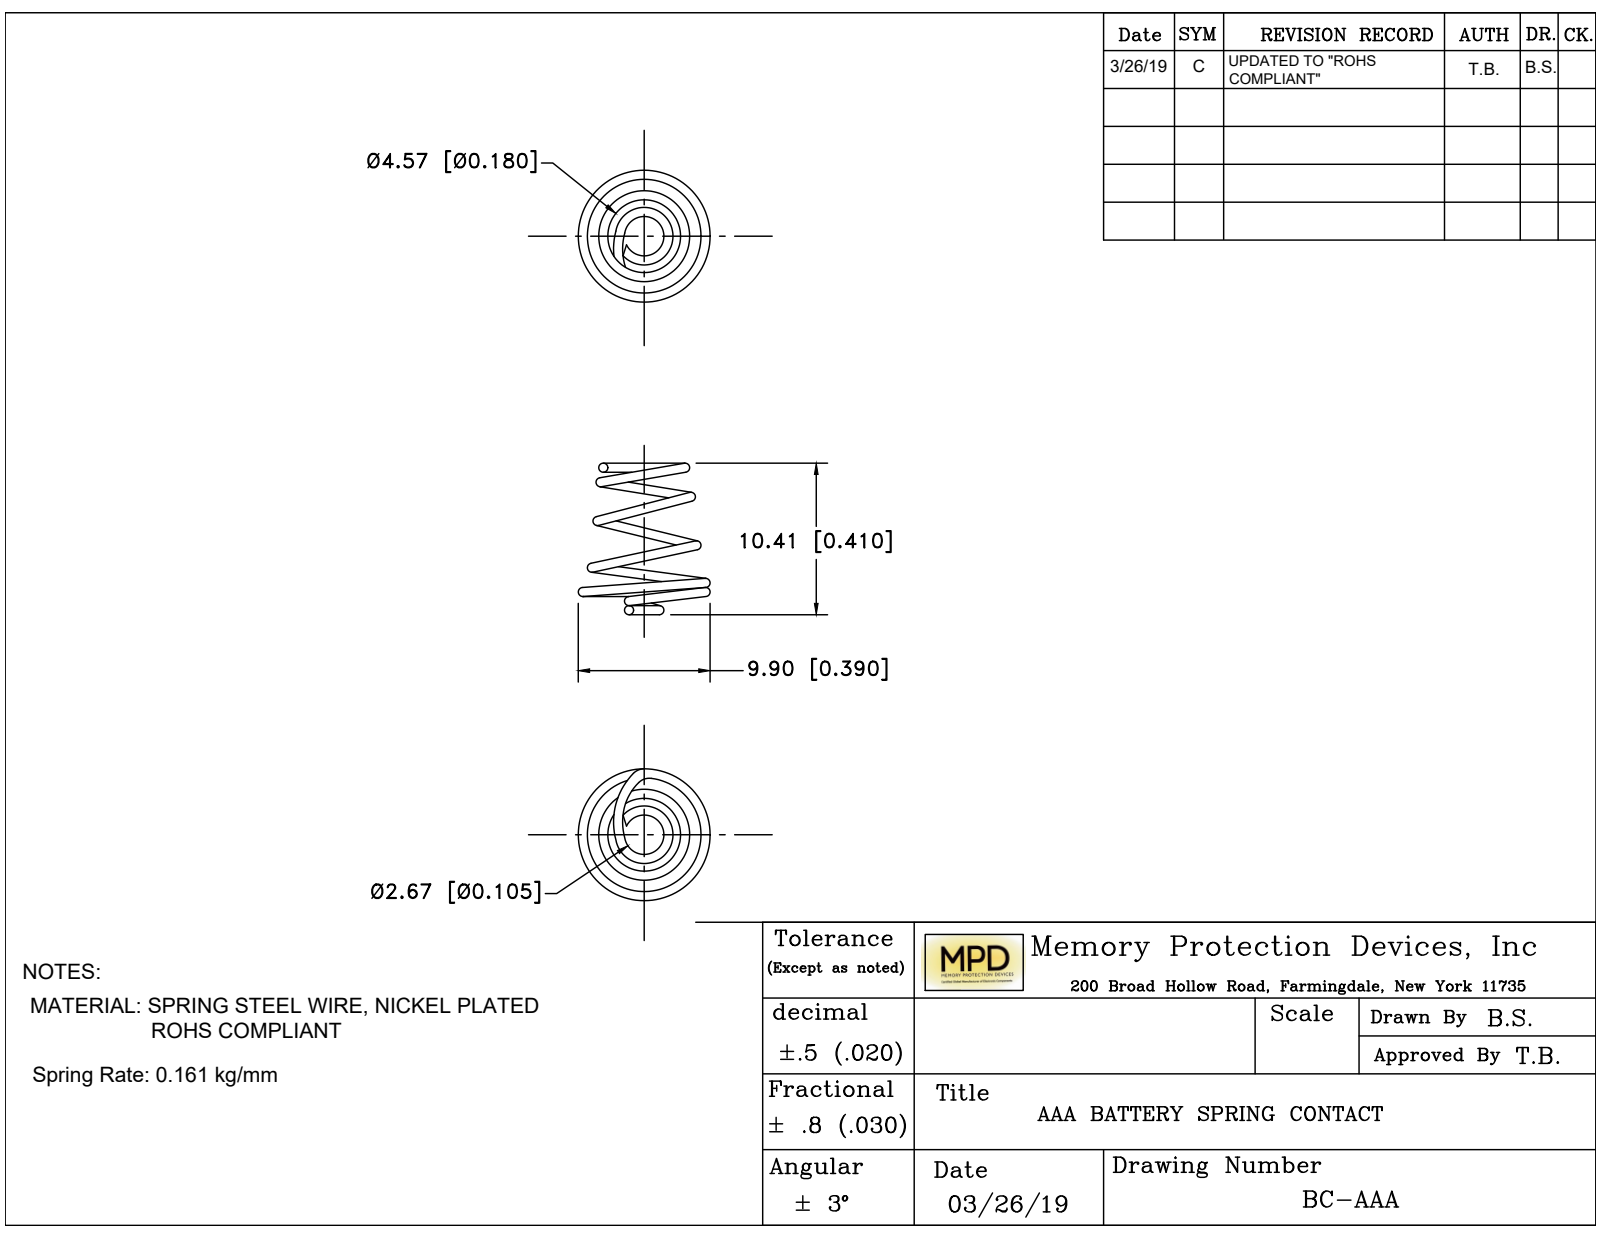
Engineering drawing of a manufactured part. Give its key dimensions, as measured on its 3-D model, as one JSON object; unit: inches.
{"part_name": "BCAAA", "step_written_by": "SolidWorks 2017 (AUTOMOTIVE_DESIGN)", "units": "inches", "bodies": {"solids": 1, "faces": 14, "planar": 2, "cylindrical": 0, "other": 12}, "overall_size": [0.41, 0.39, 0.389], "volume_in3": 0.001, "surface_area_in2": 0.264}
